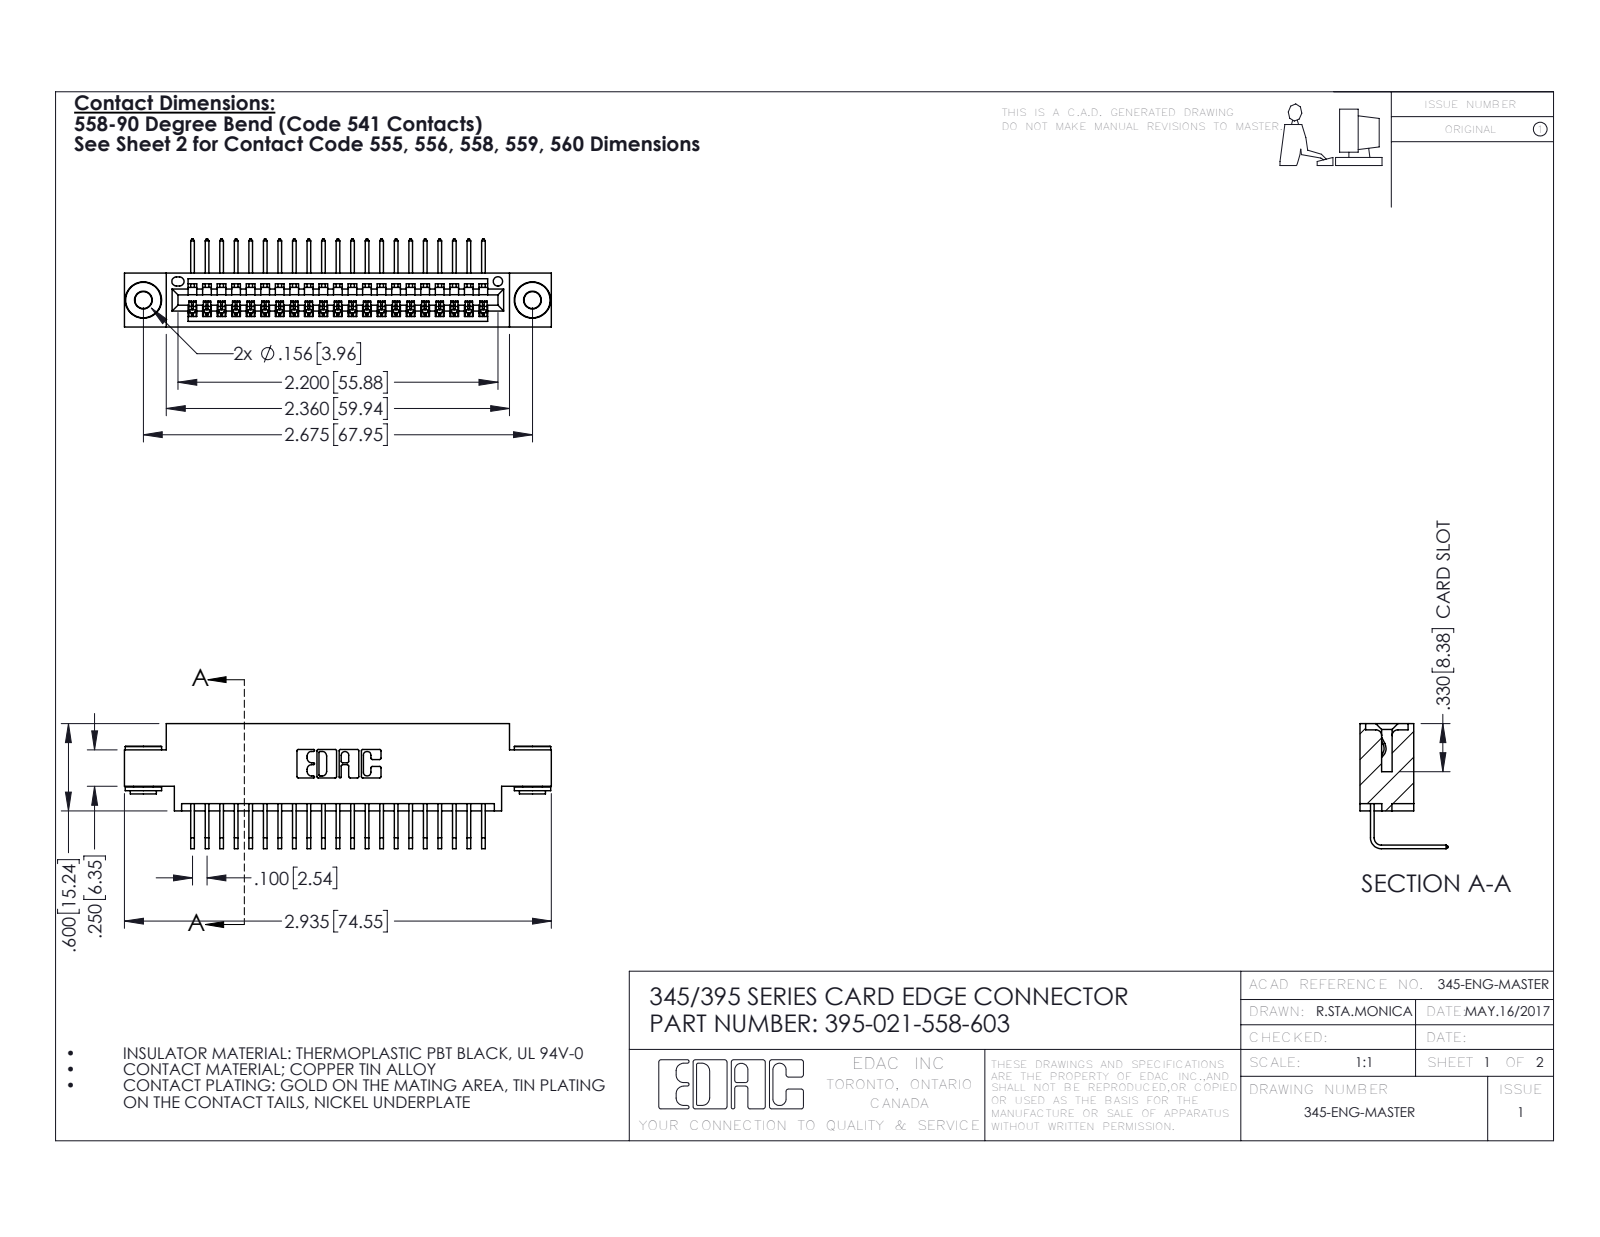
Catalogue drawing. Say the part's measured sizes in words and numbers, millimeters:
The part is named "395-021-558-603; 345 Part_0.170 Offset - 0.156 Dia-TH; 345-292-001_558 Tail - 2; 345-250-002_345-250-002-102". Its 3-D file was written by "SolidWorks 2016 (CONFIG_CONTROL_DESIGN)". It is 24 solids with 1428 faces: 976 planar, 444 cylindrical and 8 other. Overall it measures 74.5 by 21.8 by 15.4 millimeters. Its volume is 6 880 cubic millimeters and its surface area 9 613 square millimeters. Round holes: 2 of diameter 2.9, 2 of diameter 4, 1 of diameter 1.6. Round bosses or shafts: 2 of diameter 6.4, 2 of diameter 4.6, 2 of diameter 3.5. Partial cylindrical surfaces (rounded edges, fillets, slot ends): 42 of radius 0.2, 22 of radius 0.3, 6 of radius 0.2, 6 of radius 0.8, 3 of radius 0.7, 2 of radius 0.8, 2 of radius 1, 1 of radius 0.4. The main face-to-face distances are 1.8, 7.6, 9.4, 5.1, 2.5, 6.9, 0.6, 5.7, 4.4, 2.5. The hole center spacings are 6.9, 62, 67.9.
